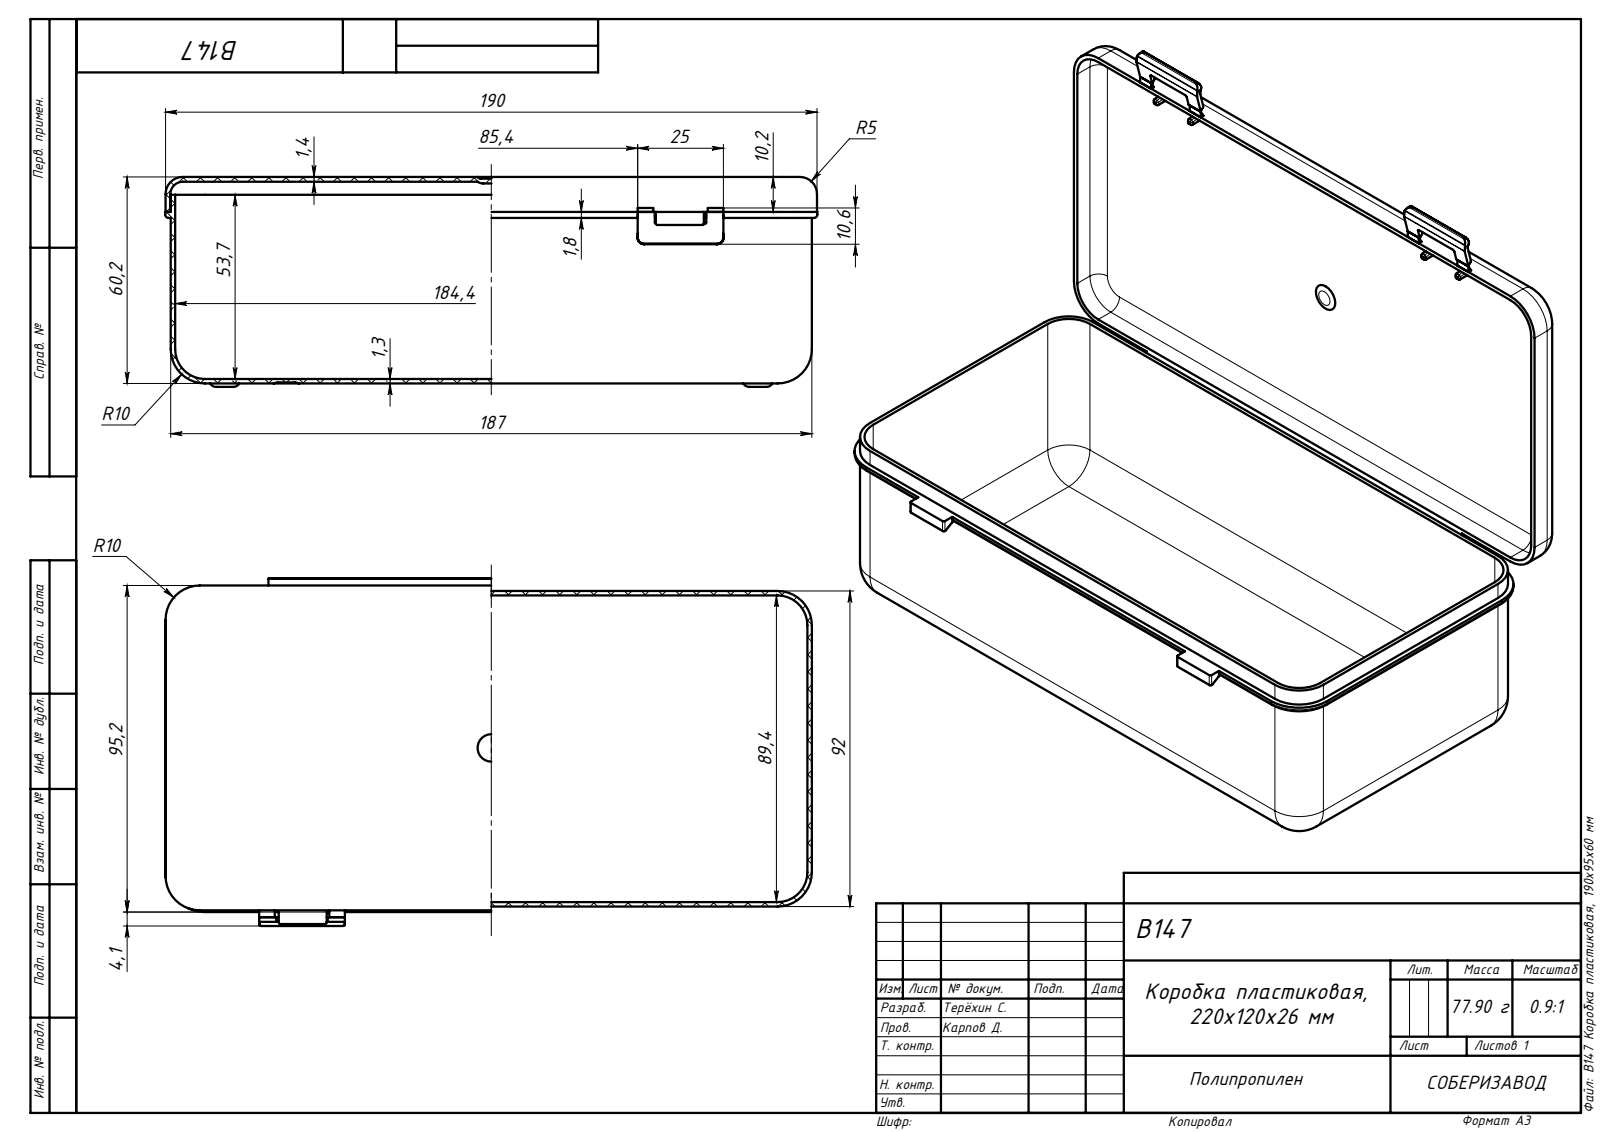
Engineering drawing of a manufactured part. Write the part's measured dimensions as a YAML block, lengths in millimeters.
part_name: "B147 Крышка_12; B147 Емкость_00; B147 Коробка пластиковая, 190x95x60 мм; B147 Защёлка_00"
step_written_by: "SolidWorks 2019 (AUTOMOTIVE_DESIGN)"
units: millimeters
bodies: {solids: 10, faces: 317, planar: 131, cylindrical: 126, other: 60}
overall_size: [190.2, 101.27, 61.2]
volume: 90052
surface_area: 136524
partial_cylinders:
  - {radius: 0.5, count: 53}
  - {radius: 10, count: 12}
  - {radius: 8.7, count: 8}
  - {radius: 1, count: 4}
  - {radius: 2, count: 4}
  - {radius: 3.6, count: 4}
  - {radius: 5, count: 4}
  - {radius: 8.6, count: 4}
face_to_face_distances: [1.3, 1.4, 90.7, 57.5, 58.9, 58.8, 60.2, 89.4, 92, 185.7]
